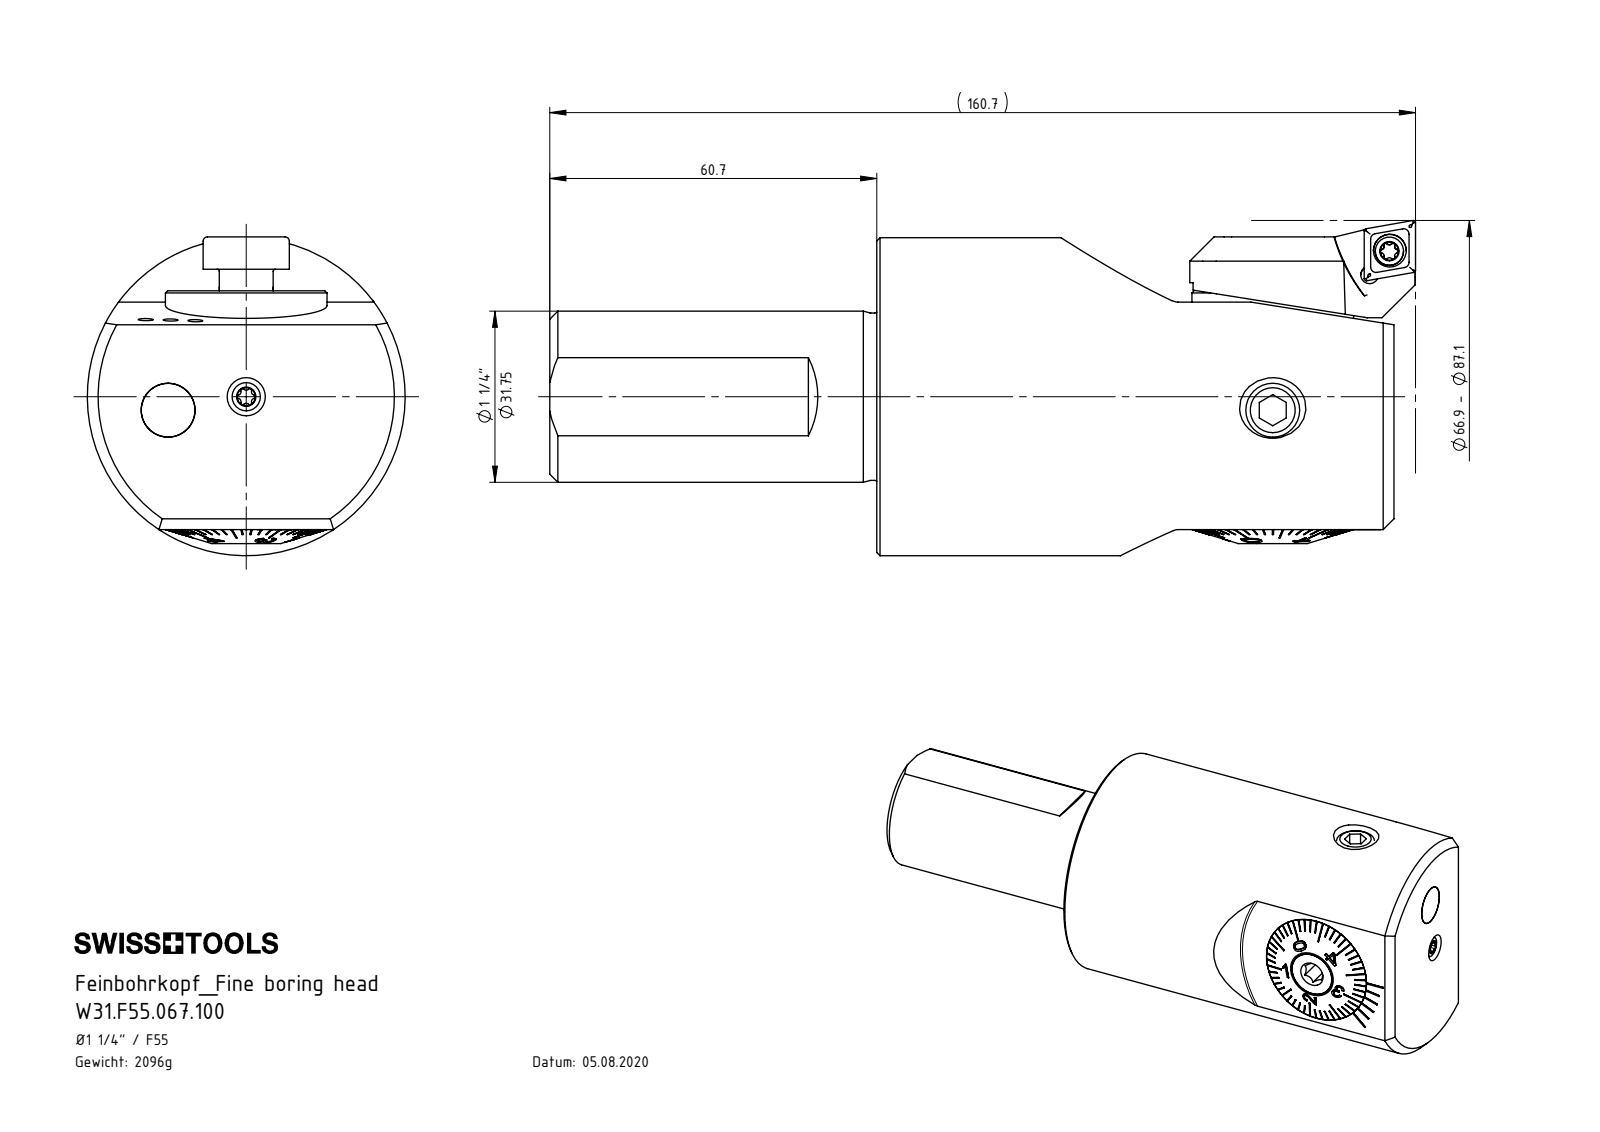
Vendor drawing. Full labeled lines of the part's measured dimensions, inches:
Part name (STEP PRODUCT): W31-F55.K20.100_B; A55-BG3.011.033_A_gekürzt; F55-BG1.011.036; WCB-ER2.001.009_A (+8 more)
STEP written by: SolidWorks 2022 (CONFIG_CONTROL_DESIGN)
Units: inches
Bodies: 15 solids, 817 faces (320 planar, 169 cylindrical, 328 other)
Overall size (bounding box): 6.327 × 2.402 × 2.165
Volume: 15.39 in³ · Surface area: 83.87 in²
Round holes (diameter × count): ⌀0.13 ×7, ⌀0.335 ×2, ⌀0.081 ×1, ⌀0.083 ×1, ⌀0.11 ×1, ⌀0.152 ×1, ⌀0.165 ×1, ⌀0.197 ×1, ⌀0.315 ×1, ⌀0.394 ×1, ⌀0.421 ×1, ⌀0.433 ×1
Round bosses / shafts (diameter × count): ⌀2.165 ×1, ⌀1.25 ×1, ⌀1.222 ×1, ⌀1.18 ×1, ⌀1.177 ×1, ⌀0.984 ×1, ⌀0.709 ×1, ⌀0.63 ×1
Partial cylindrical surfaces — rounded edges, fillets, slot ends (radius × count): R0.008 ×6, R0.013 ×6, R0.023 ×6, R0.014 ×5, R0.02 ×4, R0.126 ×3, R0.394 ×2, R0.014 ×1
Main face-to-face distances: 3.78, 0.098, 0.278, 0.232, 0.046, 1.419, 1.65, 1.697, 1.552, 0.133
Hole centre spacings: 0.154, 0.159, 0.383, 0.571, 0.827, 1.28
